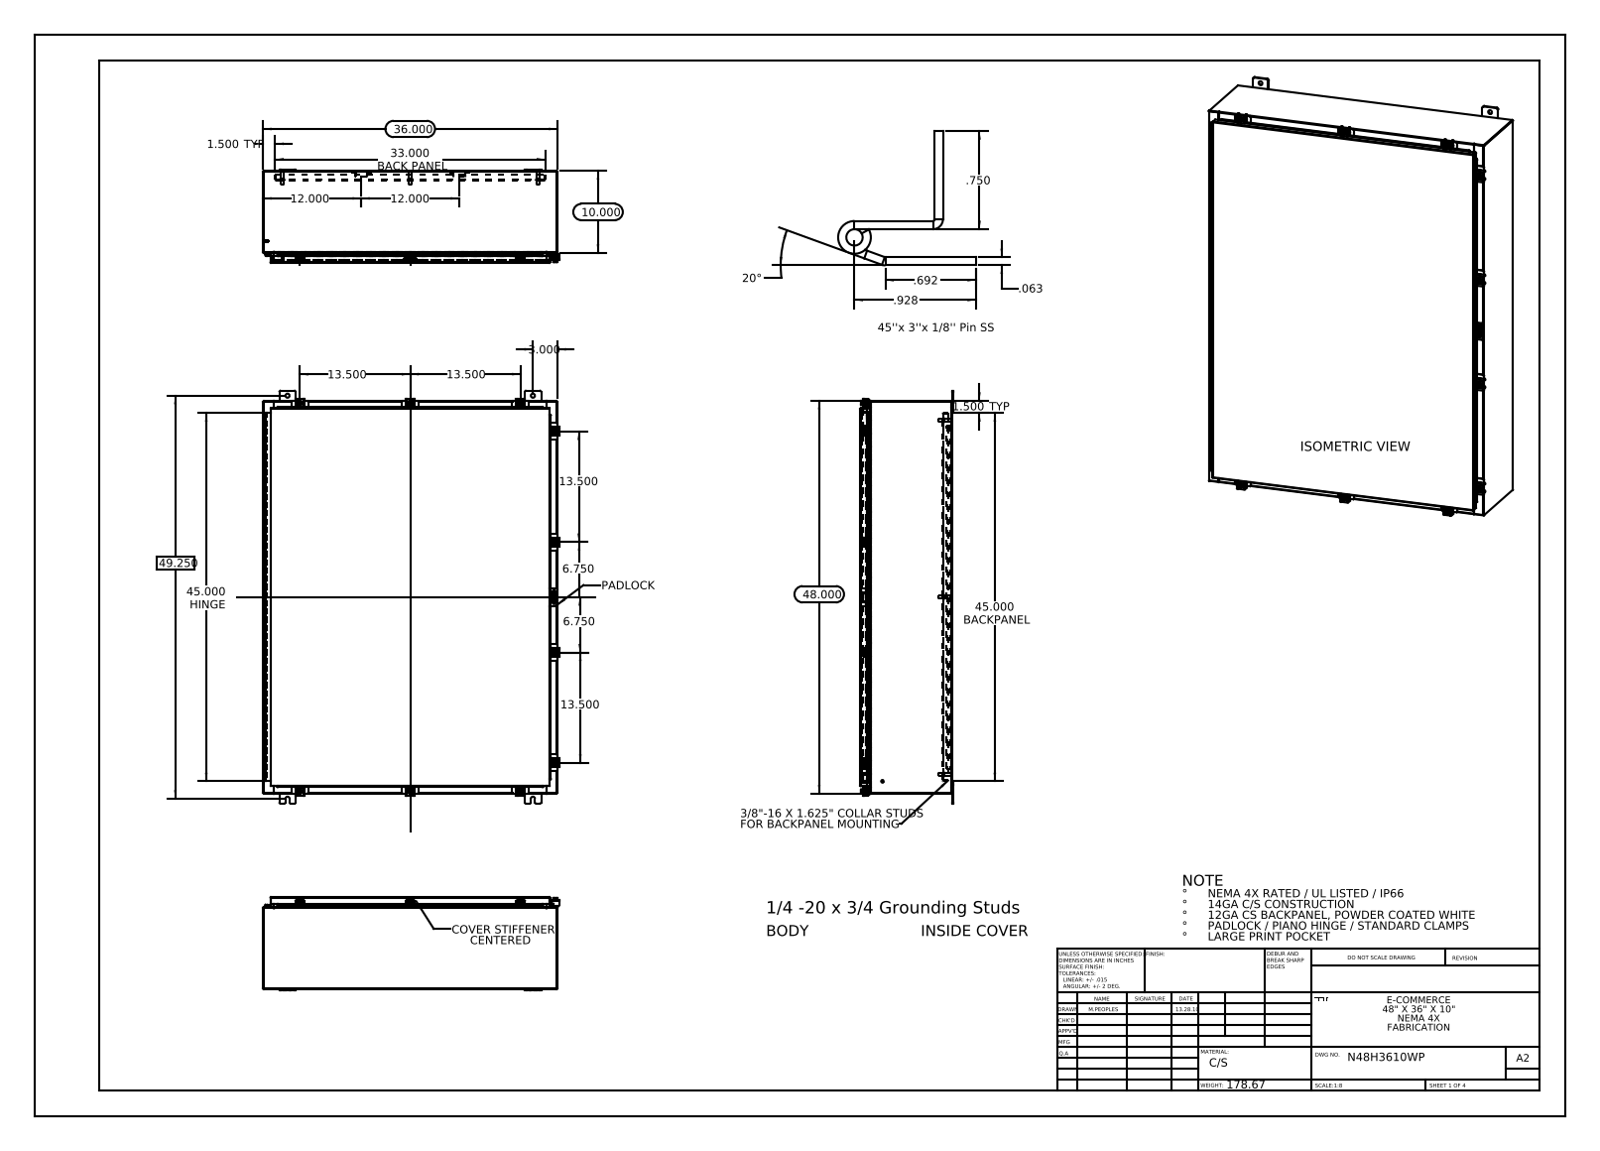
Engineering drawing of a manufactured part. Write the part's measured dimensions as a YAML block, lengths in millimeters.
part_name: "N48H3610SSWP Enclosure Stiffener; N48H3610SSWP Top; N48H3610SSWP Padlock Hasp; N48H3610SSWP Padlock Staple (+8 more)"
step_written_by: "SolidWorks 2013 (CONFIG_CONTROL_DESIGN)"
units: millimeters
bodies: {solids: 82, faces: 3115, planar: 1586, cylindrical: 1301, other: 228}
overall_size: [1282.7, 919.8, 289.3]
volume: 10260000
surface_area: 10060000
round_holes:
  - {diameter: 12.7, count: 12}
  - {diameter: 5.4, count: 10}
  - {diameter: 6.6, count: 10}
  - {diameter: 6.4, count: 6}
  - {diameter: 3.2, count: 2}
round_bosses_or_shafts:
  - {diameter: 6.4, count: 11}
  - {diameter: 12.7, count: 10}
  - {diameter: 10.1, count: 10}
  - {diameter: 15.9, count: 8}
  - {diameter: 9.5, count: 8}
  - {diameter: 8.4, count: 8}
  - {diameter: 4, count: 6}
  - {diameter: 3.6, count: 6}
partial_cylinders:
  - {radius: 1.5, count: 46}
  - {radius: 0.3, count: 39}
  - {radius: 2.2, count: 33}
  - {radius: 4.8, count: 24}
  - {radius: 3, count: 20}
  - {radius: 3.6, count: 20}
  - {radius: 1.3, count: 15}
  - {radius: 2, count: 14}
face_to_face_distances: [1.9, 282.6, 280.7, 2.6, 284.5, 25.4, 257.2, 27.3, 255.3, 29.9]
hole_center_spacings: [342.9, 347, 508, 511.1, 549.3, 605, 685.8, 965.3]
